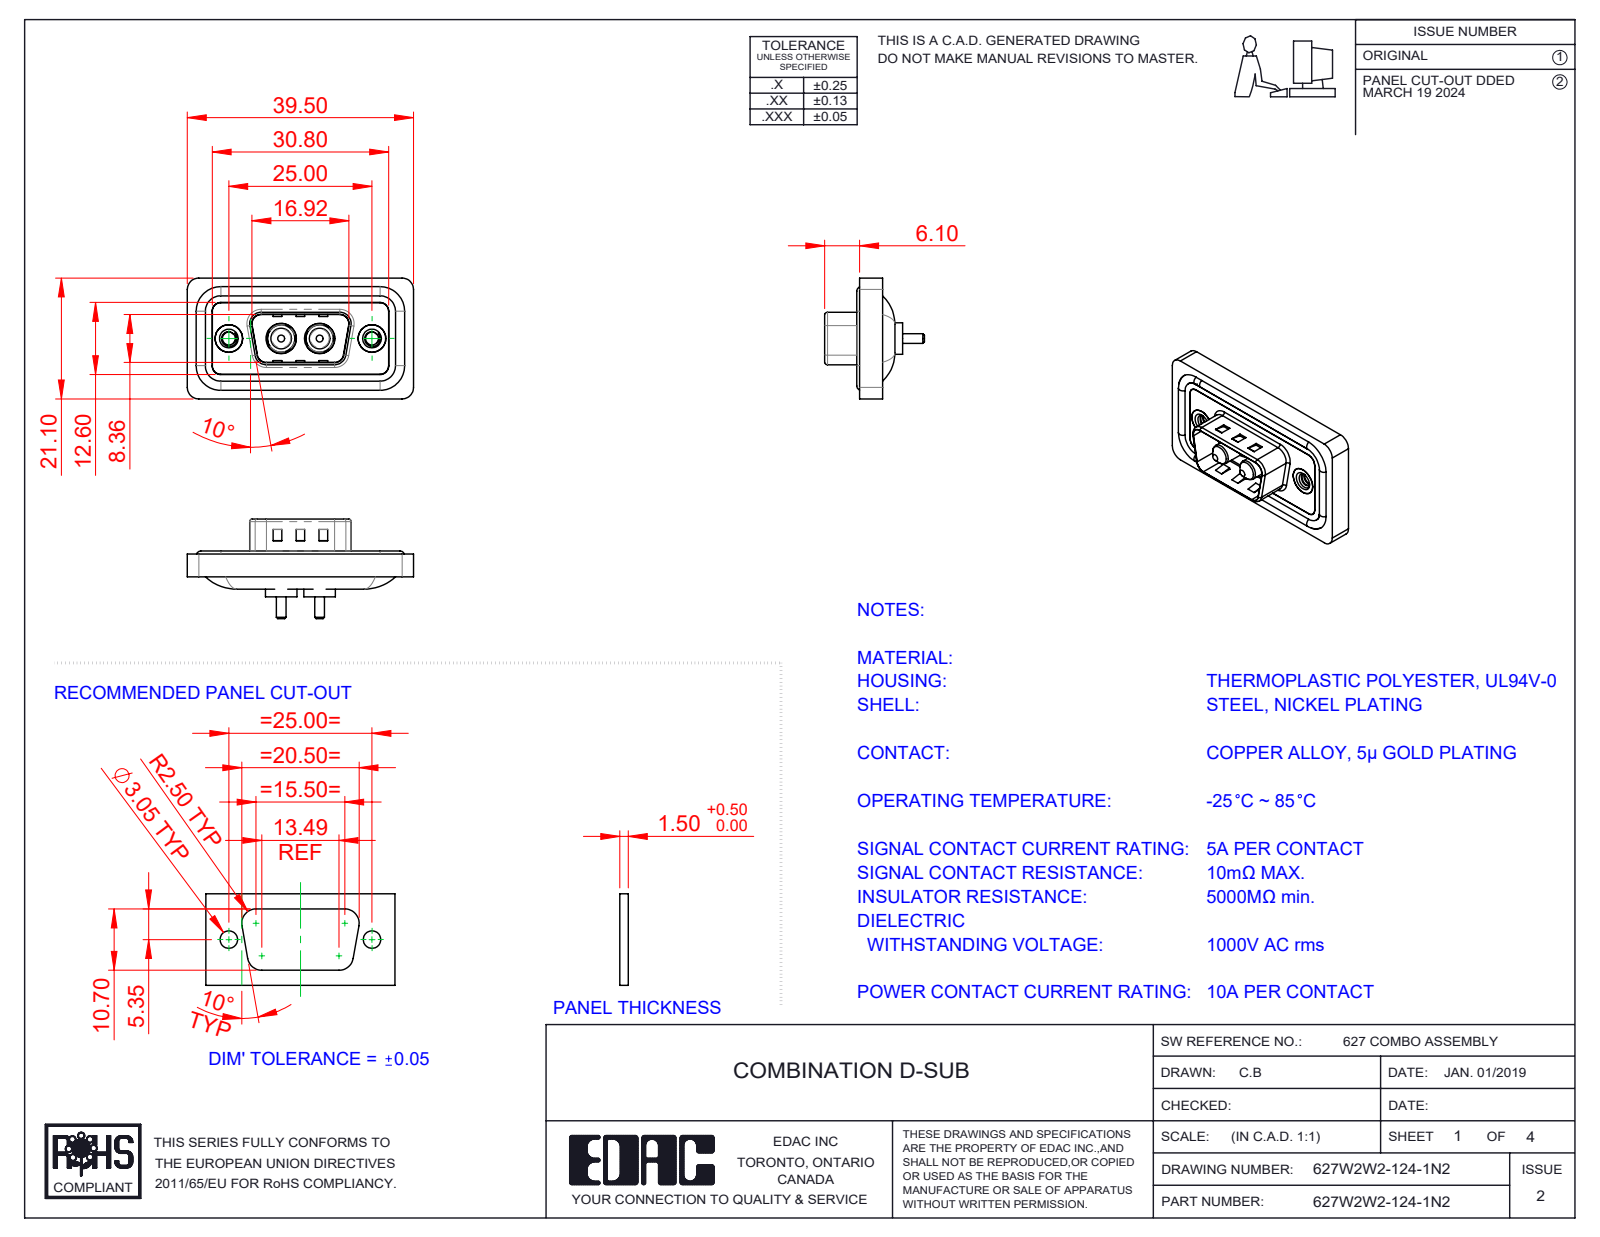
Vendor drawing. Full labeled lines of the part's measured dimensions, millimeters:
Part name (STEP PRODUCT): 627Combo Shell Front_09 Contacts; 627Combo Shell Rear_09 Contacts; Power Pin_10A S; 627Combo Threaded Rivet_2 (+3 more)
STEP written by: SolidWorks 2023 (CONFIG_CONTROL_DESIGN)
Units: millimetres
Bodies: 11 solids, 489 faces (165 planar, 218 cylindrical, 106 other)
Overall size (bounding box): 39.5 × 21.1 × 17.4
Volume: 4 431 mm³ · Surface area: 6 959 mm²
Round holes (diameter × count): ⌀2.26 ×2, ⌀4 ×2, ⌀4.8 ×2, ⌀4.85 ×2, ⌀5 ×2, ⌀5.3 ×2
Round bosses / shafts (diameter × count): ⌀1.6 ×4, ⌀5.5 ×2, ⌀5.2 ×2, ⌀4.9 ×2, ⌀4.75 ×2, ⌀3.75 ×2, ⌀3.6 ×2, ⌀1.7 ×2
Partial cylindrical surfaces — rounded edges, fillets, slot ends (radius × count): R1.5 ×22, R2 ×18, R0.5 ×8, R1.6 ×8, R0.25 ×4, R0.6 ×4, R0.65 ×4, R0.9 ×4
Main face-to-face distances: 0.4, 1.1, 2.9, 3.1, 0.5, 1.5, 1.6, 4, 2.5, 0.7
Hole centre spacings: 9.14, 15.86, 6.72, 25
